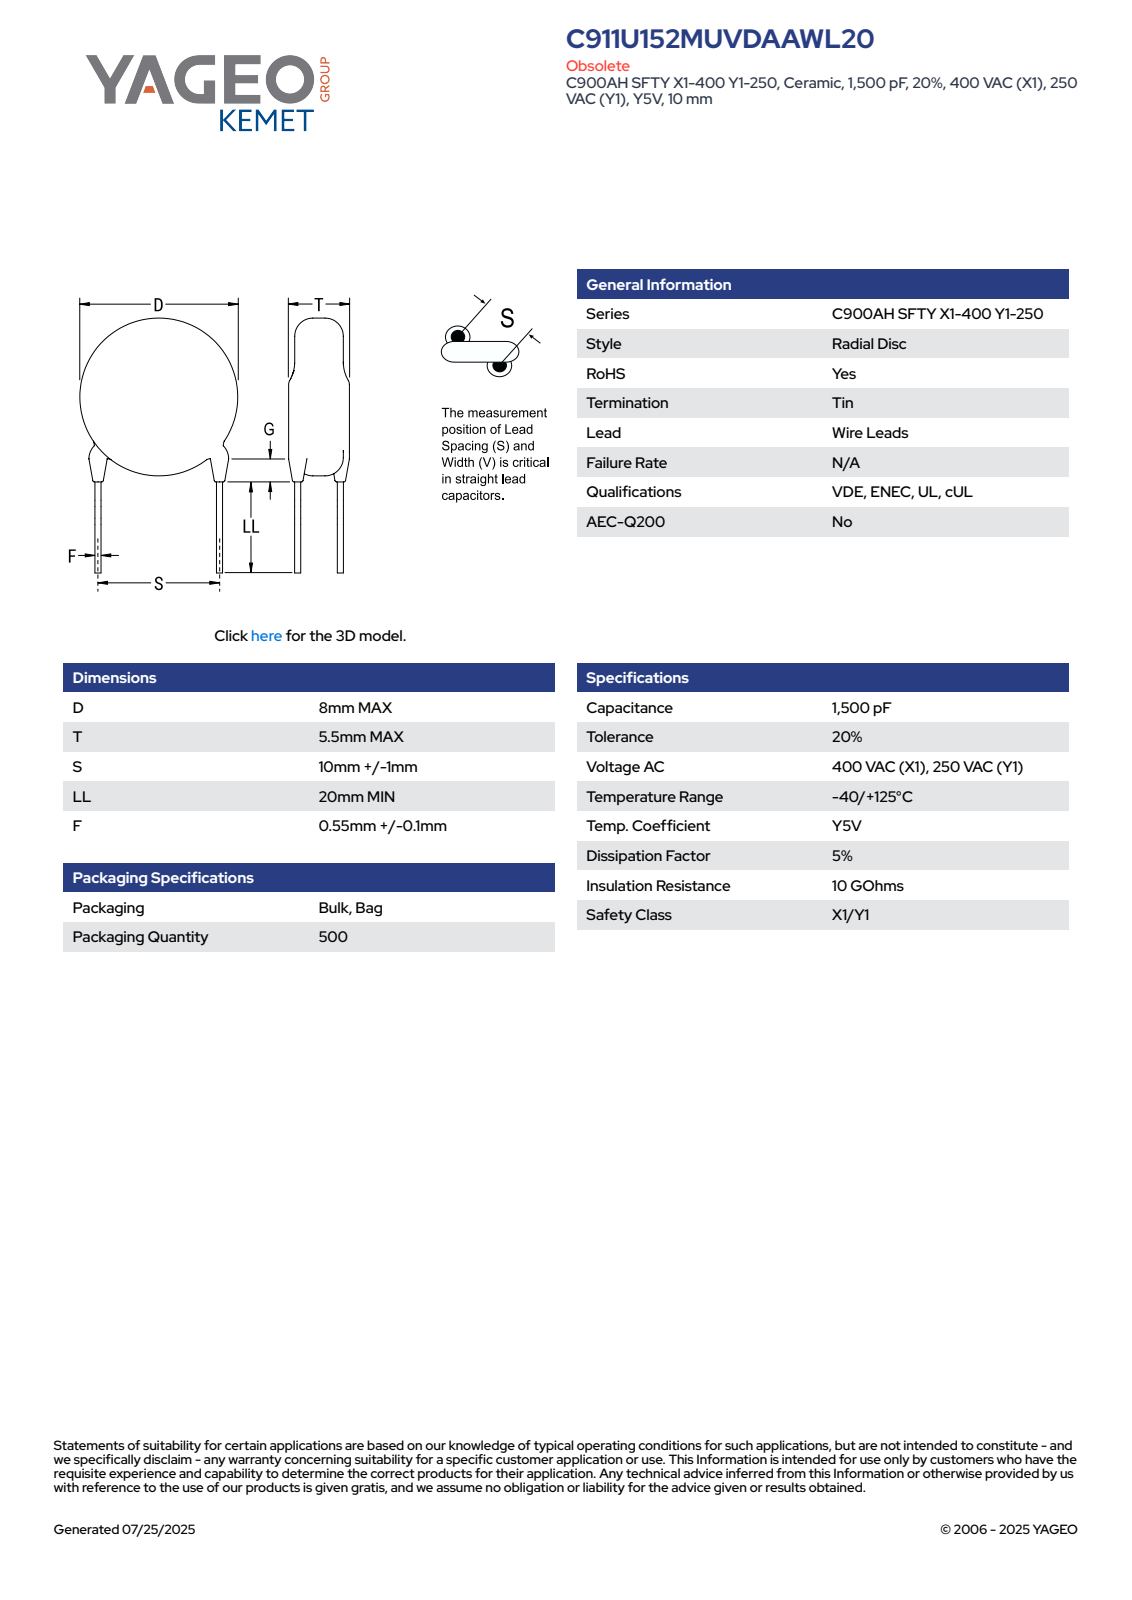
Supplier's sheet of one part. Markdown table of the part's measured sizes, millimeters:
| quantity | value |
| --- | --- |
| part name | CCD_STC900_D8T5.5S10LL20F0.65G3 |
| STEP written by | SolidWorks 2014 (AUTOMOTIVE_DESIGN) |
| units | millimeters |
| bodies | 4 solids, 83 faces (61 planar, 6 cylindrical, 16 other) |
| overall size | 28.41 × 9.99 × 5.5 |
| volume | 284 mm³ |
| surface area | 318 mm² |
| round bosses / shafts (diameter × count) | 0.65 × 2, 8 × 1 |
| main face-to-face distances | 5.5, 24.87, 23.95, 0.92, 0.4, 1.04, 3.77, 0.57, 2.73, 2.84 |
